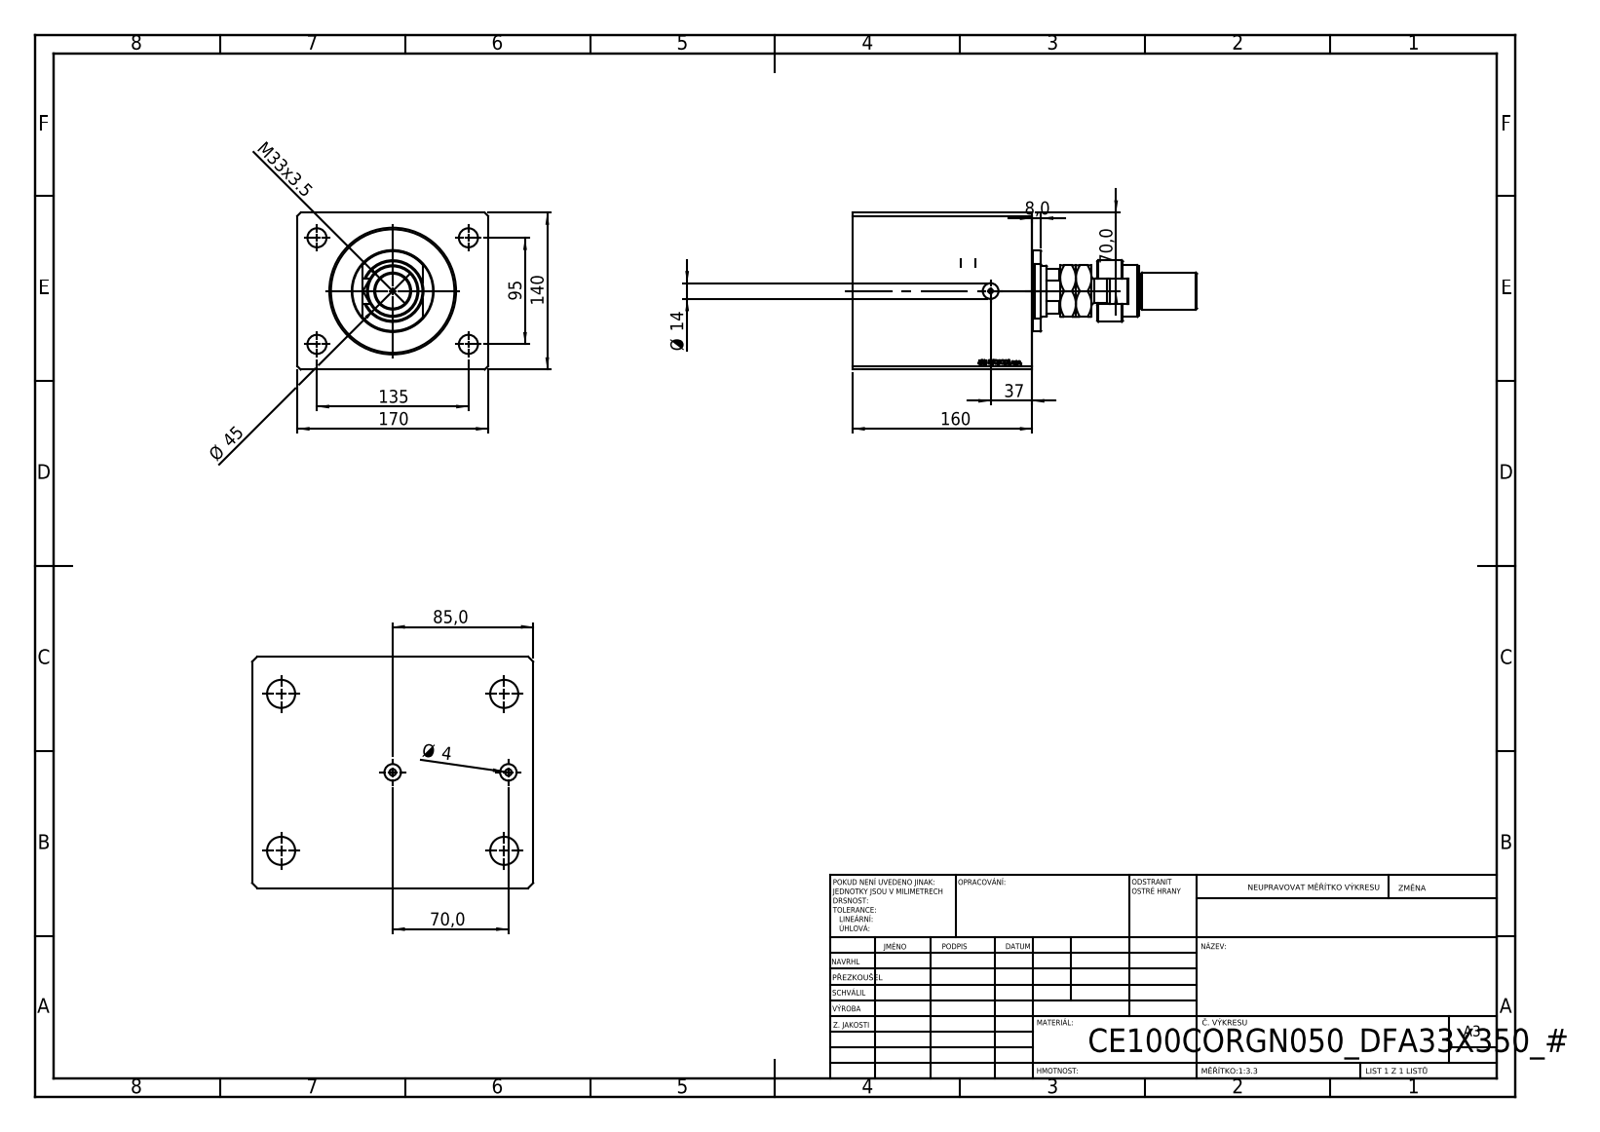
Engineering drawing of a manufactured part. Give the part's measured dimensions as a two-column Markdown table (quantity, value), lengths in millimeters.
| quantity | value |
| --- | --- |
| part name | V250CE_VC_C; MFA; V250CE_C_VCP; FEMALE_PART_FOR_DFA (+1 more) |
| STEP written by | SolidWorks 2019 (CONFIG_CONTROL_DESIGN) |
| units | millimeters |
| bodies | 5 solids, 953 faces (456 planar, 59 cylindrical, 438 other) |
| overall size | 307 × 170 × 140 |
| volume | 3 514 000 mm³ |
| surface area | 338 601 mm² |
| round holes (diameter × count) | 4 × 4, 17 × 4, 10 × 2, 14 × 2, 1.25 × 1, 31.5 × 1, 39 × 1, 45 × 1, 100 × 1, 113 × 1 |
| round bosses / shafts (diameter × count) | 72 × 1, 55 × 1, 46 × 1, 35 × 1, 33 × 1, 31 × 1, 22 × 1 |
| partial cylindrical surfaces (radius × count) | 11.5 × 1, 22 × 1 |
| main face-to-face distances | 140, 170, 160, 28.9, 131.1, 25, 135, 106.1, 50, 85 |
| hole center spacings | 82.54, 47.57, 95, 135, 145.47, 165.08, 70, 86 |
